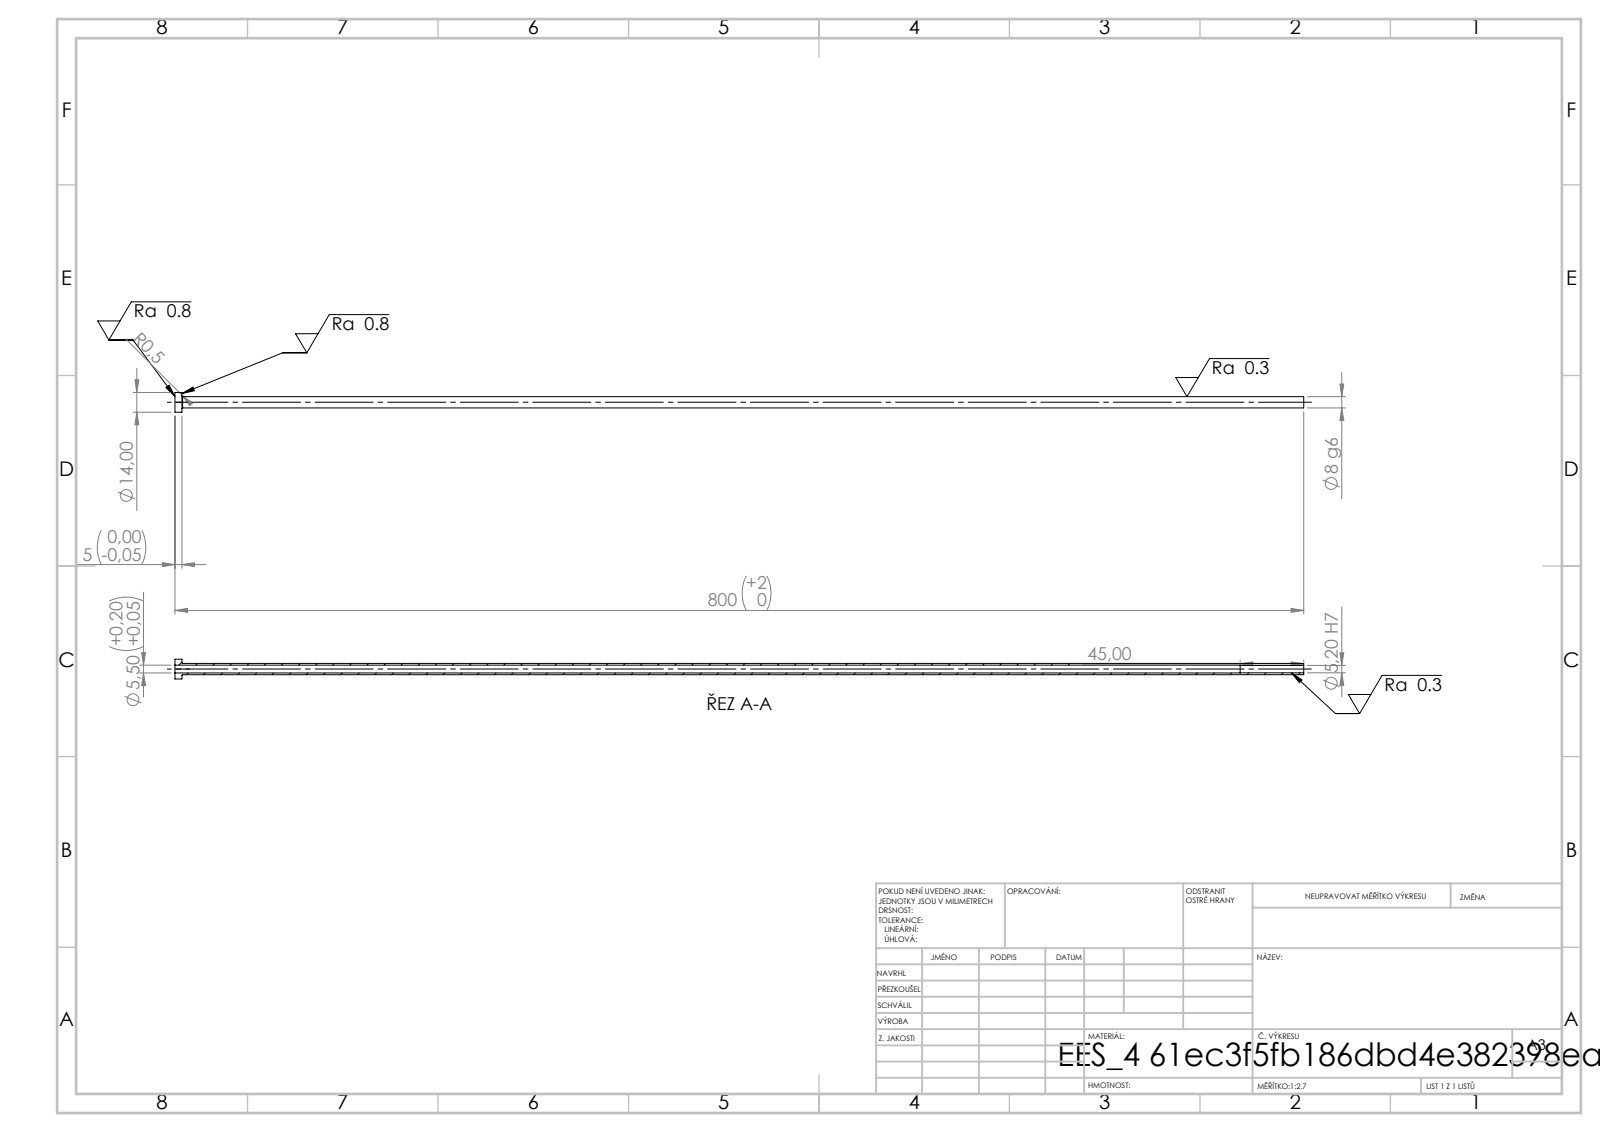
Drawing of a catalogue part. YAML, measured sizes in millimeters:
step_written_by: "SolidWorks 2019 (CONFIG_CONTROL_DESIGN)"
units: millimeters
bodies: {solids: 1, faces: 14, planar: 4, cylindrical: 8, other: 2}
overall_size: [800, 14, 14]
volume: 21839
surface_area: 34241
round_holes:
  - {diameter: 5.2, count: 1}
  - {diameter: 5.5, count: 1}
round_bosses_or_shafts:
  - {diameter: 14, count: 1}
  - {diameter: 8, count: 1}
face_to_face_distances: [5, 800, 795, 755, 750, 45]
